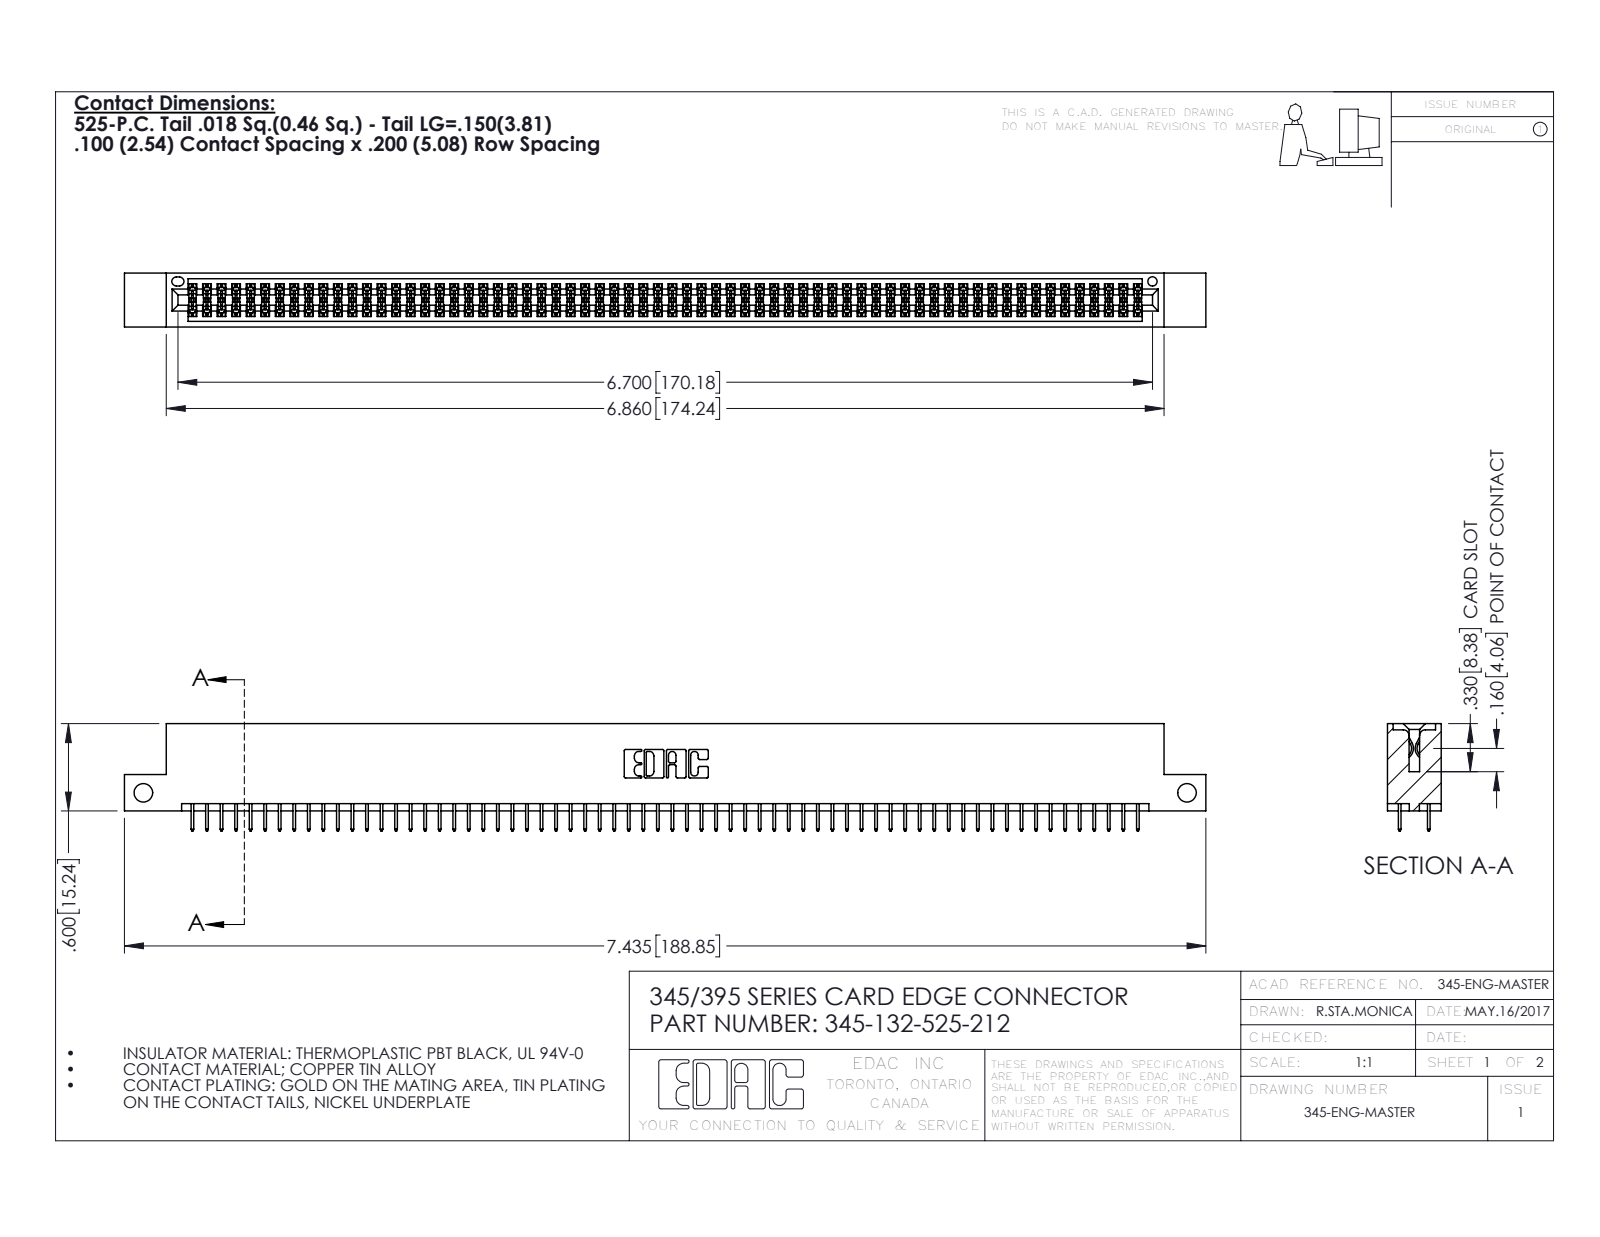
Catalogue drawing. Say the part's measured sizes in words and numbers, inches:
The part is named "345 Part_Flush Mounting Lugs - Side Mount; 345-292-001_345-293-125; 345-132-525-212". Its 3-D file was written by "SolidWorks 2020 (CONFIG_CONTROL_DESIGN)". It is 133 solids with 7254 faces: 5228 planar, 2026 cylindrical and 0 other. Overall it measures 7.435 by 0.737 by 0.37 inches. Its volume is 1.114 cubic inches and its surface area 41.34 square inches. Round holes: 2 of diameter 0.128, 1 of diameter 0.064. Partial cylindrical surfaces (rounded edges, fillets, slot ends): 264 of radius 0.006, 22 of radius 0.01, 6 of radius 0.007, 6 of radius 0.031, 3 of radius 0.026, 2 of radius 0.014, 2 of radius 0.019, 2 of radius 0.022. The main face-to-face distances are 0.298, 0.072, 0.2, 0.37, 0.098, 0.272, 0.025, 0.225, 0.072, 0.175. The hole center spacings are 7.175.
